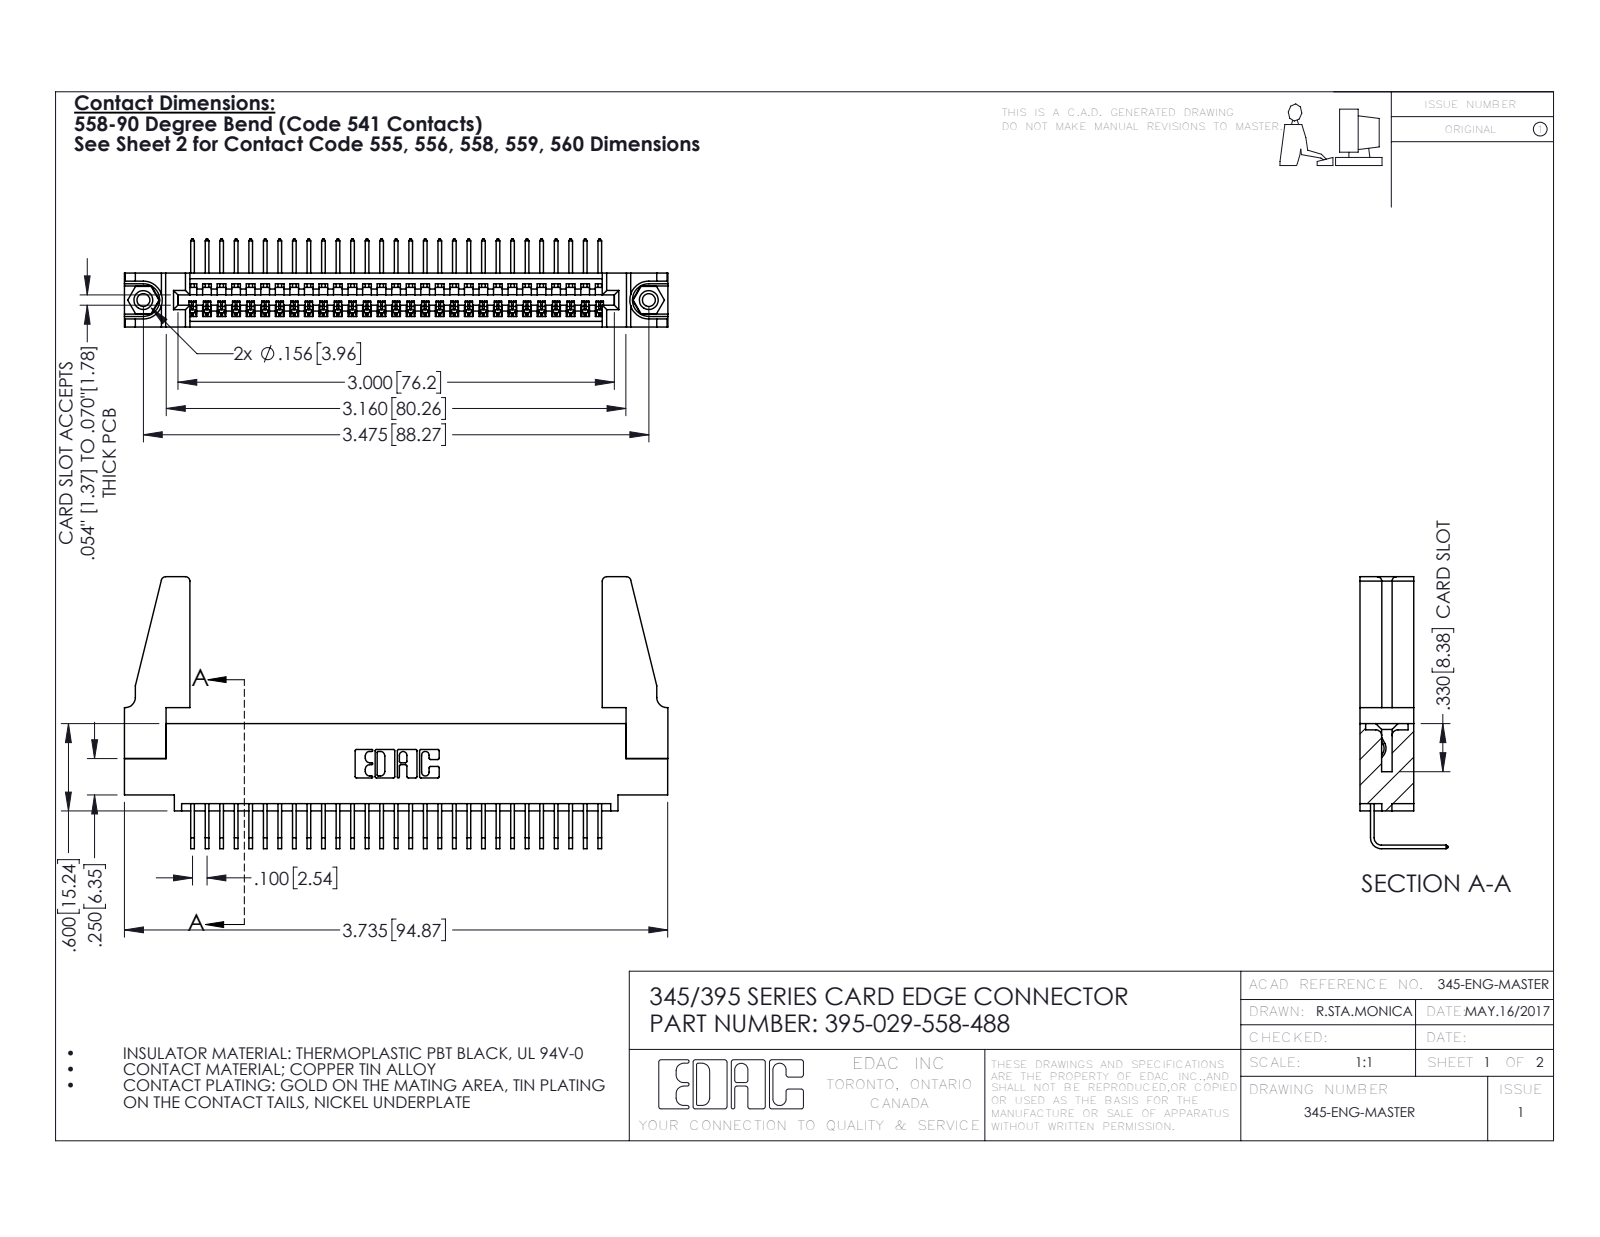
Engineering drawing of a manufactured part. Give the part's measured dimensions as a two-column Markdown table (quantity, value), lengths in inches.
| quantity | value |
| --- | --- |
| part name | 345-220-078_345-220-088; 345-250-001_345-250-001-102; 345-292-001_558 Tail - 2; 345 Part_0.110 Offset - 0.156 Dia-TH (+1 more) |
| STEP written by | SolidWorks 2016 (CONFIG_CONTROL_DESIGN) |
| units | inches |
| bodies | 34 solids, 1994 faces (1374 planar, 604 cylindrical, 16 other) |
| overall size | 3.736 × 1.869 × 0.605 |
| volume | 0.743 in³ |
| surface area | 23.98 in² |
| round holes (diameter × count) | 0.089 × 2, 0.125 × 2, 0.156 × 2, 0.064 × 1 |
| round bosses / shafts (diameter × count) | 0.155 × 2 |
| partial cylindrical surfaces (radius × count) | 0.006 × 58, 0.01 × 22, 0.03 × 8, 0.007 × 6, 0.031 × 6, 0.026 × 3, 0.031 × 2, 0.04 × 2 |
| main face-to-face distances | 0.072, 0.37, 0.298, 0.2, 0.098, 0.272, 0.025, 0.225, 0.149, 0.072 |
| hole center spacings | 0.27, 3.24, 3.475 |
